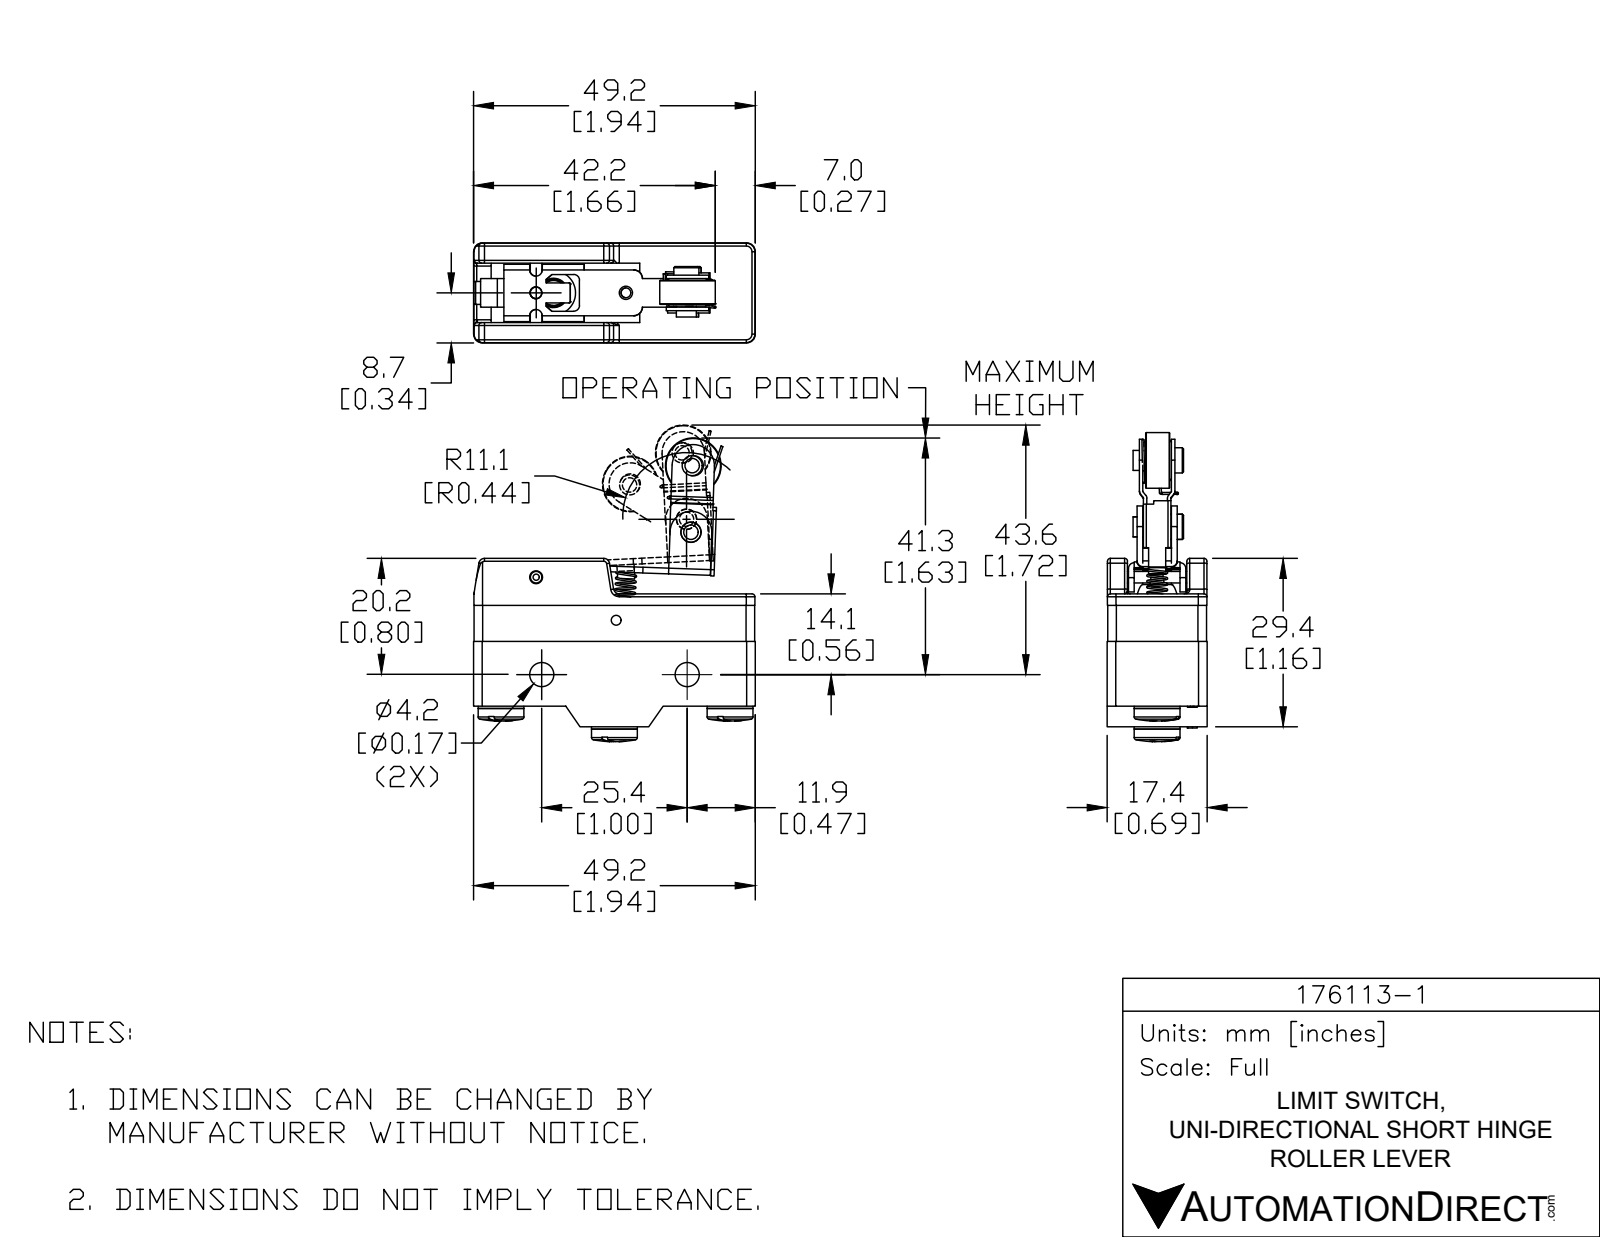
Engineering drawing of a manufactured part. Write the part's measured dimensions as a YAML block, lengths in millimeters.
part_name: "176-MS (Screw Terminal)-Uni Directional Short Hinge Roller Lever"
step_written_by: "SolidWorks 2018 (AUTOMOTIVE_DESIGN)"
units: millimeters
bodies: {solids: 17, faces: 686, planar: 295, cylindrical: 193, other: 198}
overall_size: [54.4, 49.2, 17.4]
volume: 18520
surface_area: 11840
round_holes:
  - {diameter: 3.8, count: 3}
  - {diameter: 6, count: 3}
  - {diameter: 1.7, count: 2}
  - {diameter: 2, count: 2}
  - {diameter: 2.5, count: 2}
  - {diameter: 3.6, count: 2}
  - {diameter: 4.2, count: 2}
  - {diameter: 4.5, count: 2}
  - {diameter: 4.6, count: 1}
  - {diameter: 5, count: 1}
round_bosses_or_shafts:
  - {diameter: 0.3, count: 4}
  - {diameter: 8, count: 3}
  - {diameter: 4.4, count: 2}
  - {diameter: 3.5, count: 2}
  - {diameter: 9.7, count: 1}
  - {diameter: 5.5, count: 1}
  - {diameter: 3, count: 1}
  - {diameter: 2, count: 1}
partial_cylinders:
  - {radius: 0.5, count: 21}
  - {radius: 1.5, count: 14}
  - {radius: 0.3, count: 12}
  - {radius: 1, count: 9}
  - {radius: 0.2, count: 6}
  - {radius: 0.8, count: 4}
  - {radius: 1.1, count: 3}
  - {radius: 2.9, count: 3}
face_to_face_distances: [1, 17.3, 17.6, 17.4, 2, 19.6, 3.6, 0.4, 3.5, 13.9]
hole_center_spacings: [1.9, 9.2, 10.6, 11.6, 11.6, 12.5, 15.6, 15.7]
